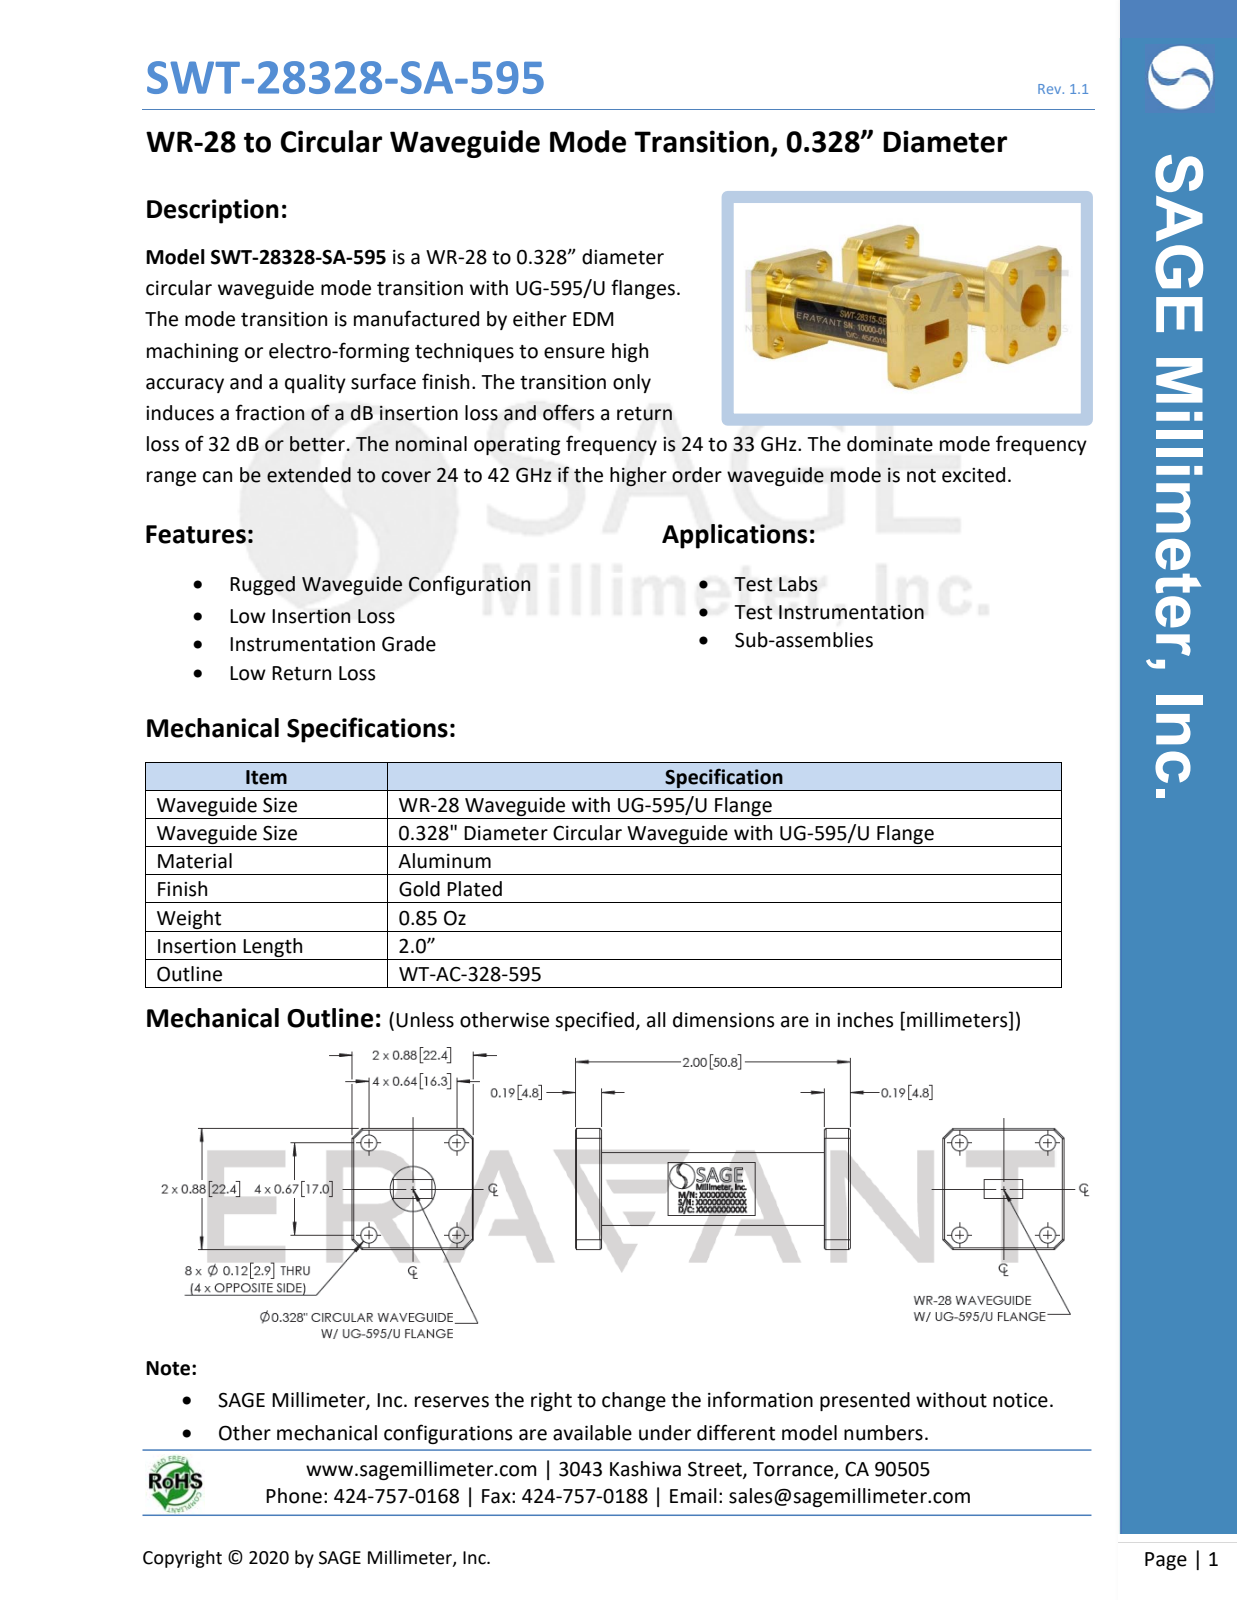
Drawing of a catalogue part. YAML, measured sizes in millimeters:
part_name: "SWT-28328-SA-595"
step_written_by: "SolidWorks 2021 (CONFIG_CONTROL_DESIGN)"
units: millimeters
bodies: {solids: 1, faces: 80, planar: 54, cylindrical: 18, other: 8}
overall_size: [50.8, 22.4, 22.4]
volume: 10300
surface_area: 4461
round_holes:
  - {diameter: 2.9, count: 4}
round_bosses_or_shafts:
  - {diameter: 13.5, count: 1}
face_to_face_distances: [4.8, 46, 50.8, 22.4, 41.1, 50.5, 4.6, 45.7, 32.5, 18.9]
hole_center_spacings: [16.3, 17, 23.5]
